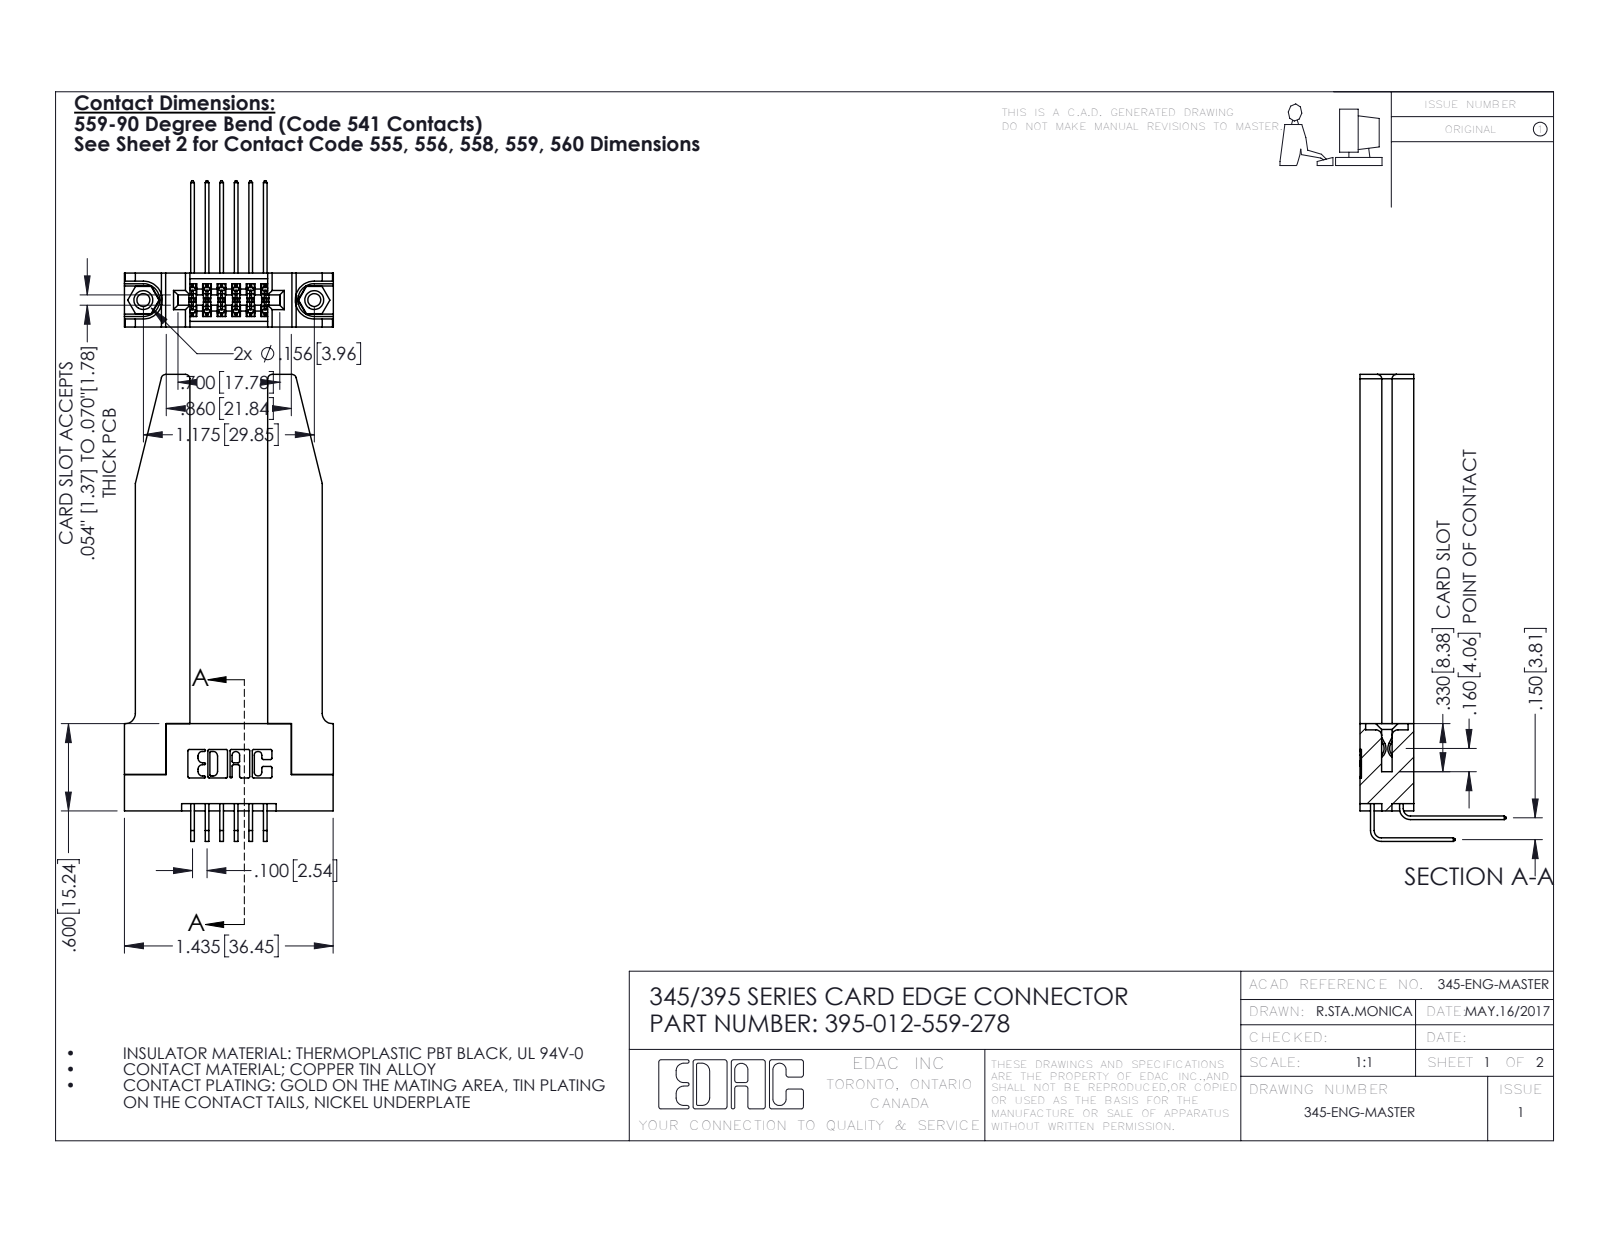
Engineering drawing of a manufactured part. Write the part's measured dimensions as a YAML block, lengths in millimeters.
part_name: "345-292-001_558 559 Tail - 1; 345-292-001_559 Tail - 2; 345-220-078_345-220-078; 345 Part_Flush Mounting Lugs - 0.156 Dia-TH (+2 more)"
step_written_by: "SolidWorks 2016 (CONFIG_CONTROL_DESIGN)"
units: millimeters
bodies: {solids: 17, faces: 984, planar: 642, cylindrical: 290, other: 52}
overall_size: [81.5, 36.5, 25.5]
volume: 11000
surface_area: 11310
round_holes:
  - {diameter: 2.3, count: 2}
  - {diameter: 3.2, count: 2}
  - {diameter: 4, count: 2}
  - {diameter: 1.6, count: 1}
round_bosses_or_shafts:
  - {diameter: 3.9, count: 2}
partial_cylinders:
  - {radius: 0.3, count: 22}
  - {radius: 0.2, count: 19}
  - {radius: 0.8, count: 8}
  - {radius: 0.2, count: 6}
  - {radius: 0.8, count: 6}
  - {radius: 0.7, count: 3}
  - {radius: 0.4, count: 2}
  - {radius: 0.5, count: 2}
face_to_face_distances: [9.4, 3.8, 5.6, 1.8, 3.8, 13.6, 2, 7.6, 5.1, 2.4]
hole_center_spacings: [6.9, 24, 29.8]
